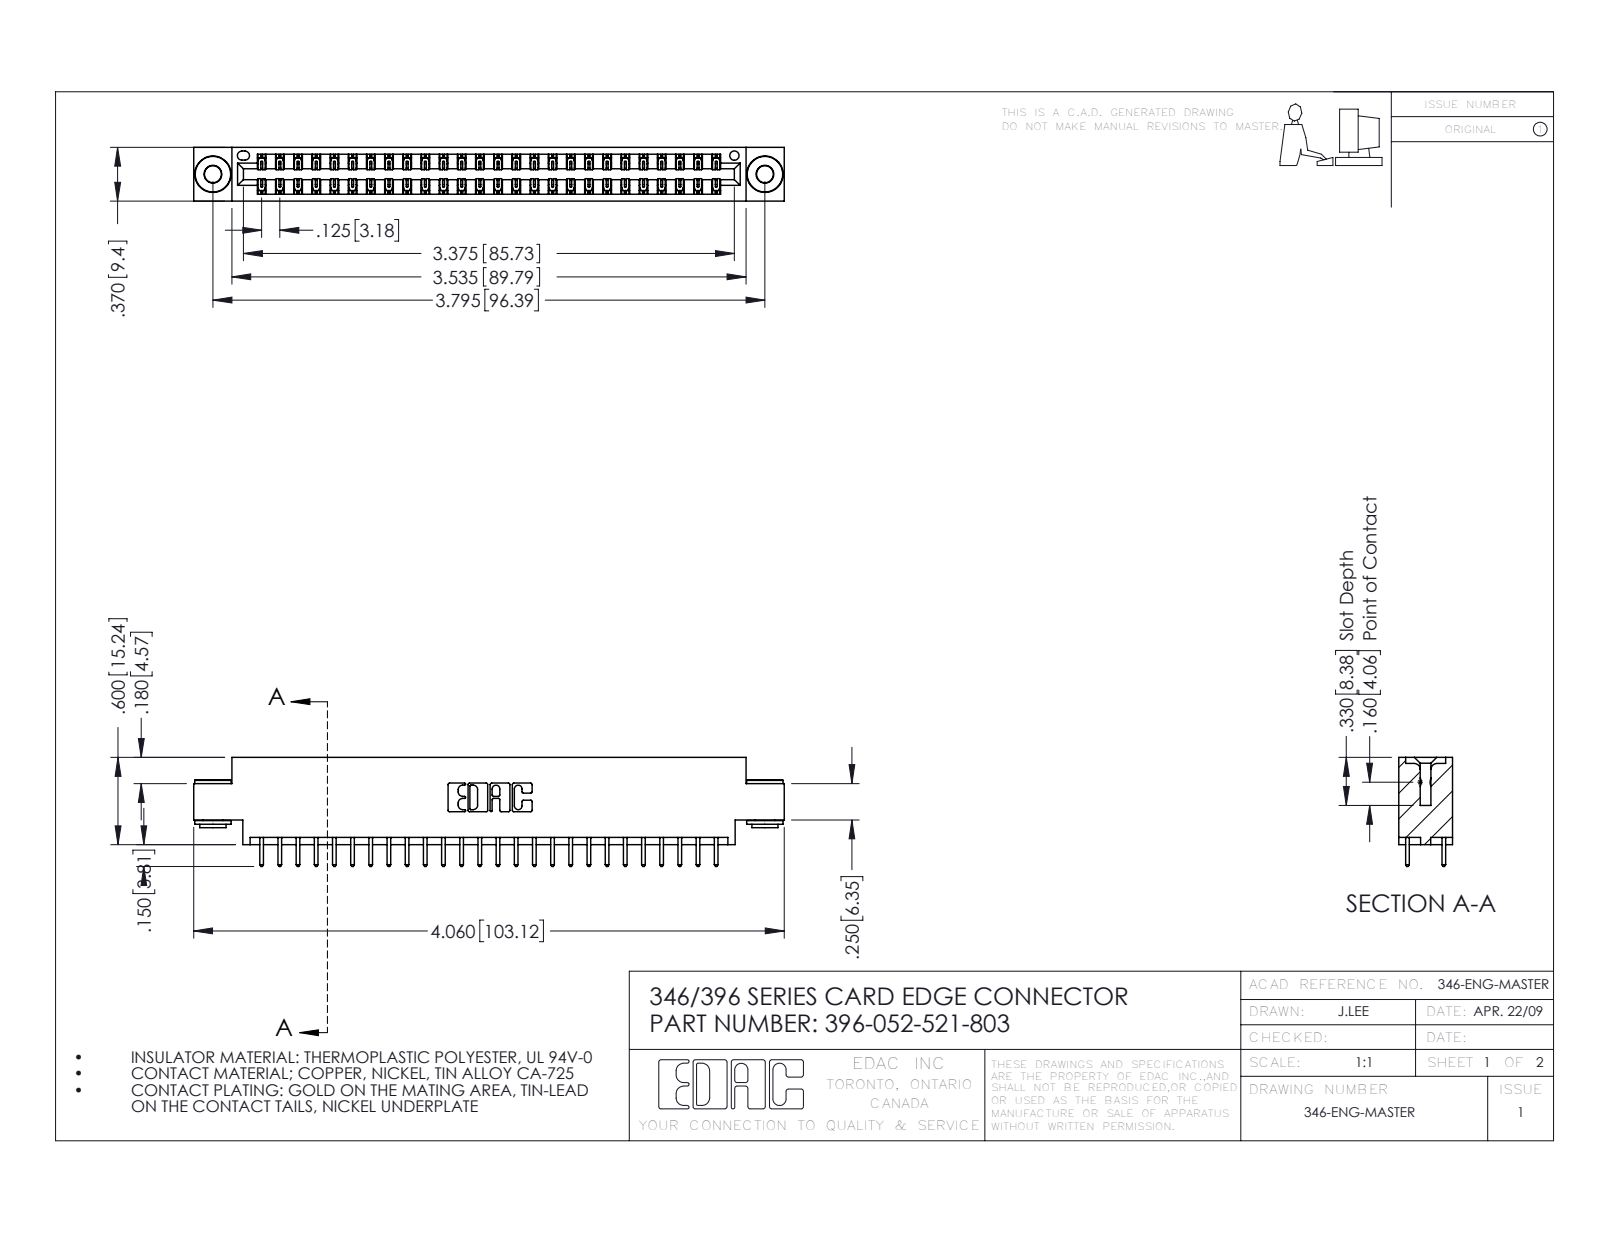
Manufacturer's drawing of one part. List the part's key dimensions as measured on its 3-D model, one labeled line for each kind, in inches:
Part name (STEP PRODUCT): 396-052-521-803; 345-250-002_345-250-002-102; 346 Part_0.170 Offset - 0.156 Dia-TH; 345-292-001_345-293-121
STEP written by: SolidWorks 2016 (CONFIG_CONTROL_DESIGN)
Units: inches
Bodies: 55 solids, 2868 faces (1910 planar, 950 cylindrical, 8 other)
Overall size (bounding box): 4.06 × 0.75 × 0.37
Volume: 0.597 in³ · Surface area: 20.83 in²
Round holes (diameter × count): ⌀0.116 ×2, ⌀0.156 ×2, ⌀0.064 ×1
Round bosses / shafts (diameter × count): ⌀0.25 ×2, ⌀0.18 ×2, ⌀0.136 ×2
Partial cylindrical surfaces — rounded edges, fillets, slot ends (radius × count): R0.006 ×78, R0.01 ×52, R0.01 ×22, R0.007 ×6, R0.031 ×6, R0.026 ×3, R0.014 ×2, R0.022 ×2
Main face-to-face distances: 0.048, 0.322, 0.37, 0.25, 0.025, 0.072, 0.298, 0.275, 0.148, 0.222
Hole centre spacings: 0.246, 3.587, 3.795
